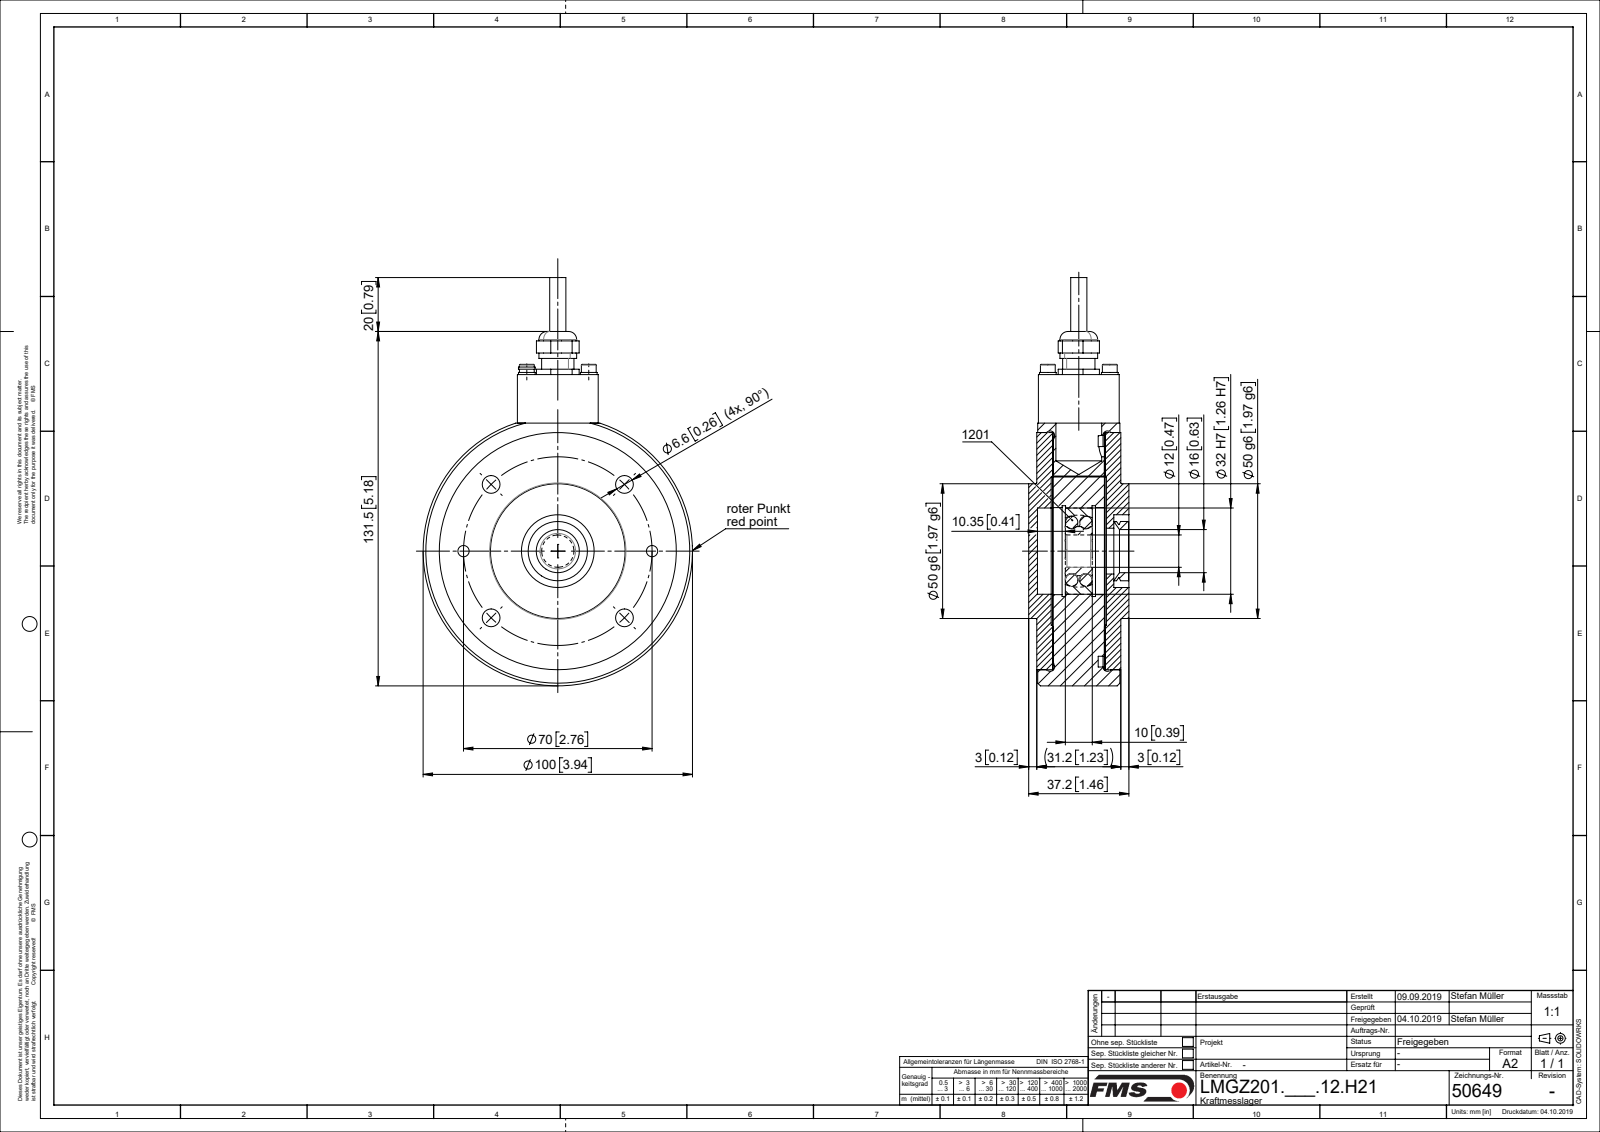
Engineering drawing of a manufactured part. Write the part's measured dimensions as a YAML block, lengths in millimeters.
part_name: "L50649_STP; L4866604; TEIL1; L48891 (+8 more)"
step_written_by: "Mechanical Desktop 2009 (CONFIG_CONTROL_DESIGN)"
units: millimeters
bodies: {solids: 20, faces: 358, planar: 117, cylindrical: 197, other: 44}
overall_size: [131.5, 100, 37.2]
volume: 237401
surface_area: 92151
round_holes:
  - {diameter: 2.6, count: 4}
  - {diameter: 3.2, count: 4}
  - {diameter: 3.4, count: 4}
  - {diameter: 6.6, count: 4}
  - {diameter: 4, count: 2}
  - {diameter: 5.5, count: 2}
  - {diameter: 10, count: 2}
  - {diameter: 17, count: 2}
  - {diameter: 6, count: 1}
  - {diameter: 11.28, count: 1}
  - {diameter: 12, count: 1}
  - {diameter: 16, count: 1}
round_bosses_or_shafts:
  - {diameter: 6.2, count: 4}
  - {diameter: 5.5, count: 4}
  - {diameter: 3, count: 4}
  - {diameter: 8, count: 2}
  - {diameter: 5, count: 2}
  - {diameter: 100, count: 1}
  - {diameter: 88, count: 1}
  - {diameter: 78, count: 1}
partial_cylinders:
  - {radius: 4, count: 1}
face_to_face_distances: [19.25, 5.85, 25.1, 6.1, 25.35, 19, 19.5, 5.5, 24.75, 0.35]
hole_center_spacings: [35, 16.26, 23, 26.79, 49.5, 64.67, 70, 32.53]
